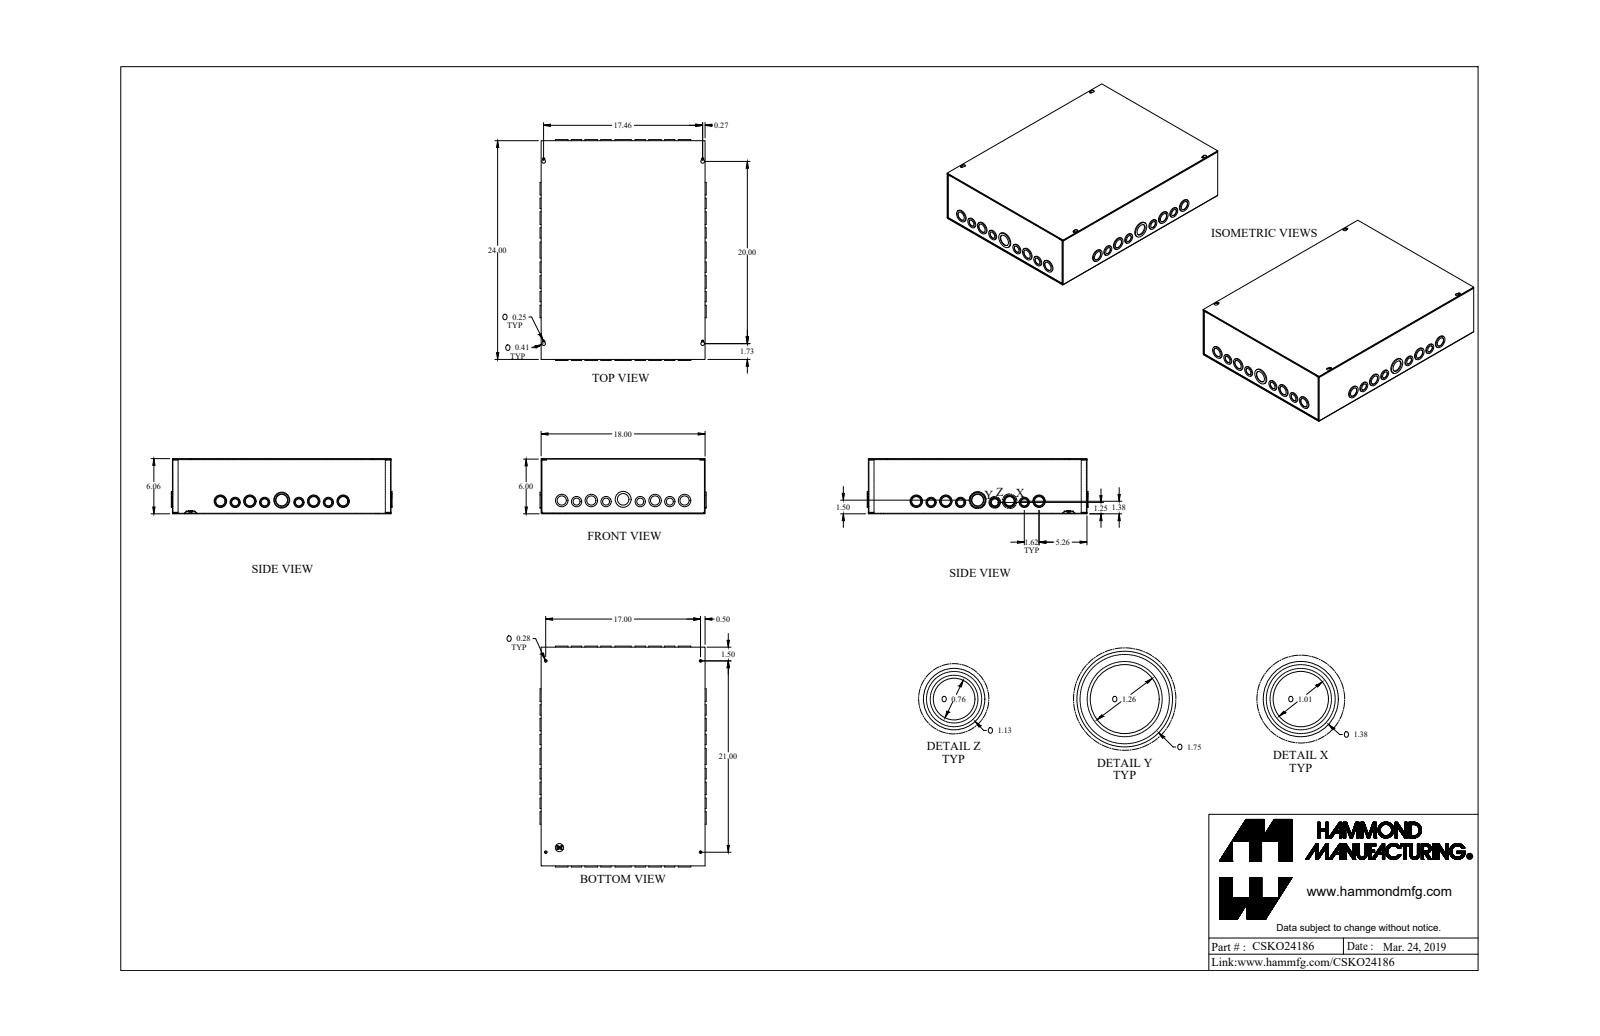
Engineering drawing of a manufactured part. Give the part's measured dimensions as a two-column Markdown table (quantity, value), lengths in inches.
| quantity | value |
| --- | --- |
| part name | CSKO24186_Default |
| STEP written by | SolidWorks 2019 (CONFIG_CONTROL_DESIGN) |
| units | inches |
| bodies | 4 solids, 637 faces (269 planar, 360 cylindrical, 8 other) |
| overall size | 24.234 × 18.234 × 6.057 |
| volume | 82.55 in³ |
| surface area | 2 914 in² |
| round holes (diameter × count) | 1.011 × 16, 1.261 × 10, 0.761 × 8, 0.17 × 5, 0.281 × 4, 1.636 × 2, 0.5 × 1 |
| round bosses / shafts (diameter × count) | 1.125 × 14, 1.375 × 9, 0.875 × 8, 0.875 × 6, 1.125 × 4, 1.375 × 3, 1.75 × 2, 0.492 × 1 |
| partial cylindrical surfaces (radius × count) | 0.029 × 12, 0.086 × 12, 0.057 × 8, 0.125 × 4, 0.203 × 4 |
| main face-to-face distances | 0.057, 6, 5.943, 6.057, 17.943, 23.943, 18, 17.886, 24, 23.886 |
| hole center spacings | 1.625, 3.24, 8.621, 7, 10.24, 0.55, 1.896, 3.502 |
